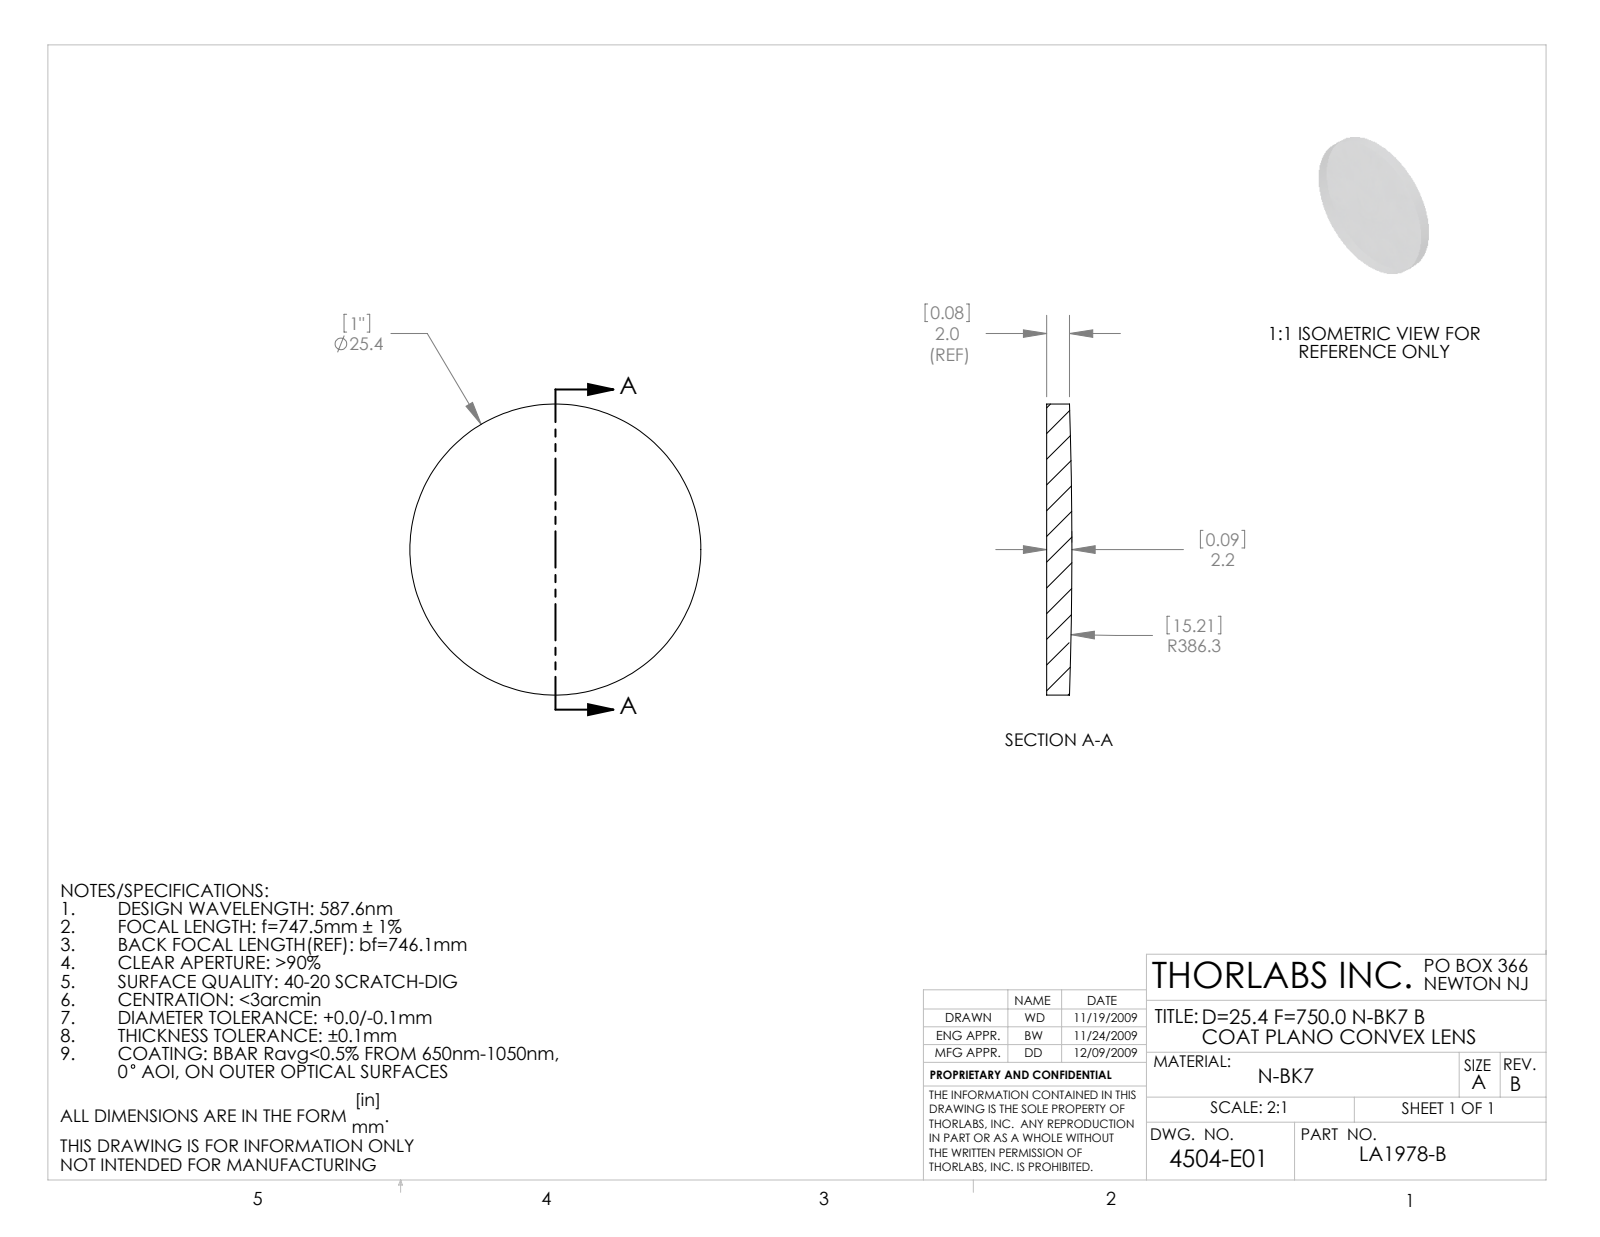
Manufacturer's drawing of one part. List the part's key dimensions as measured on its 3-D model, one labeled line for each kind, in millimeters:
Part name (STEP PRODUCT): 4504-E0W
STEP written by: SolidWorks 2009 (AUTOMOTIVE_DESIGN)
Units: millimetres
Bodies: 1 solid, 5 faces (1 planar, 2 cylindrical, 2 other)
Overall size (bounding box): 25.4 × 25.4 × 2.2
Volume: 1 062 mm³ · Surface area: 1 172 mm²
Round bosses / shafts (diameter × count): ⌀25.4 ×1
